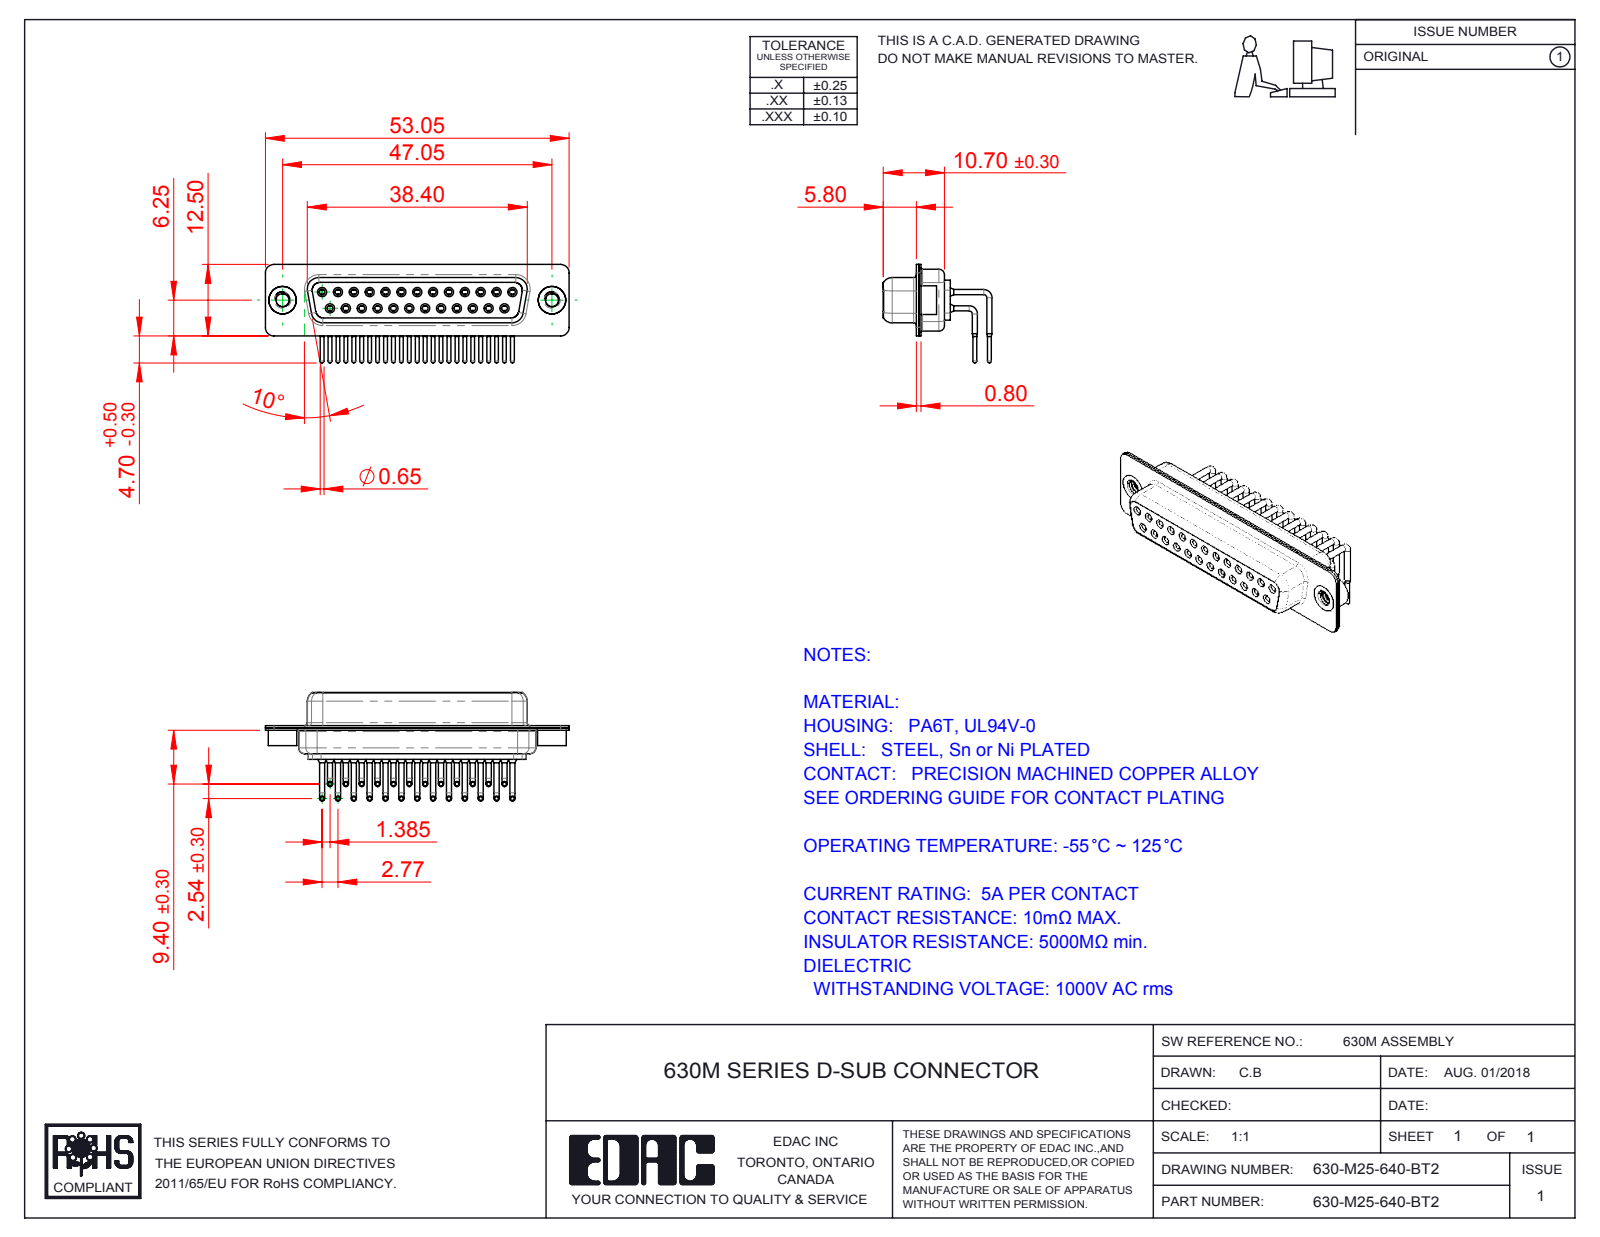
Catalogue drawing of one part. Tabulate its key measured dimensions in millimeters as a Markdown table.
| quantity | value |
| --- | --- |
| part name | 630M Contact Row 1; 630M Contact Row 2; 630M Shell Front_25 Contacts; 630M 4-40 Threaded Rivet (+3 more) |
| STEP written by | SolidWorks 2016 (CONFIG_CONTROL_DESIGN) |
| units | millimeters |
| bodies | 30 solids, 1604 faces (442 planar, 712 cylindrical, 450 other) |
| overall size | 53.05 × 18.99 × 17.2 |
| volume | 3 898 mm³ |
| surface area | 9 728 mm² |
| round holes (diameter × count) | 1 × 25, 1.1 × 25, 1.7 × 25, 1.8 × 25, 2 × 25, 2.26 × 2, 4 × 2, 4.8 × 2 |
| round bosses / shafts (diameter × count) | 0.9 × 50, 1.6 × 25, 1.5 × 25, 0.65 × 25, 5 × 2, 4.9 × 2 |
| partial cylindrical surfaces (radius × count) | 1.5 × 16, 2 × 12, 1.35 × 10, 1.6 × 8, 0.25 × 4, 0.5 × 4, 0.6 × 4, 0.65 × 4 |
| main face-to-face distances | 0.4, 1.45, 8.95, 6.2, 2.3, 1.9, 8.5, 7.05, 0.45, 0.85 |
| hole center spacings | 3.16, 2.77, 5.54, 8.31, 11.08, 13.85, 5.04, 7.49 |
